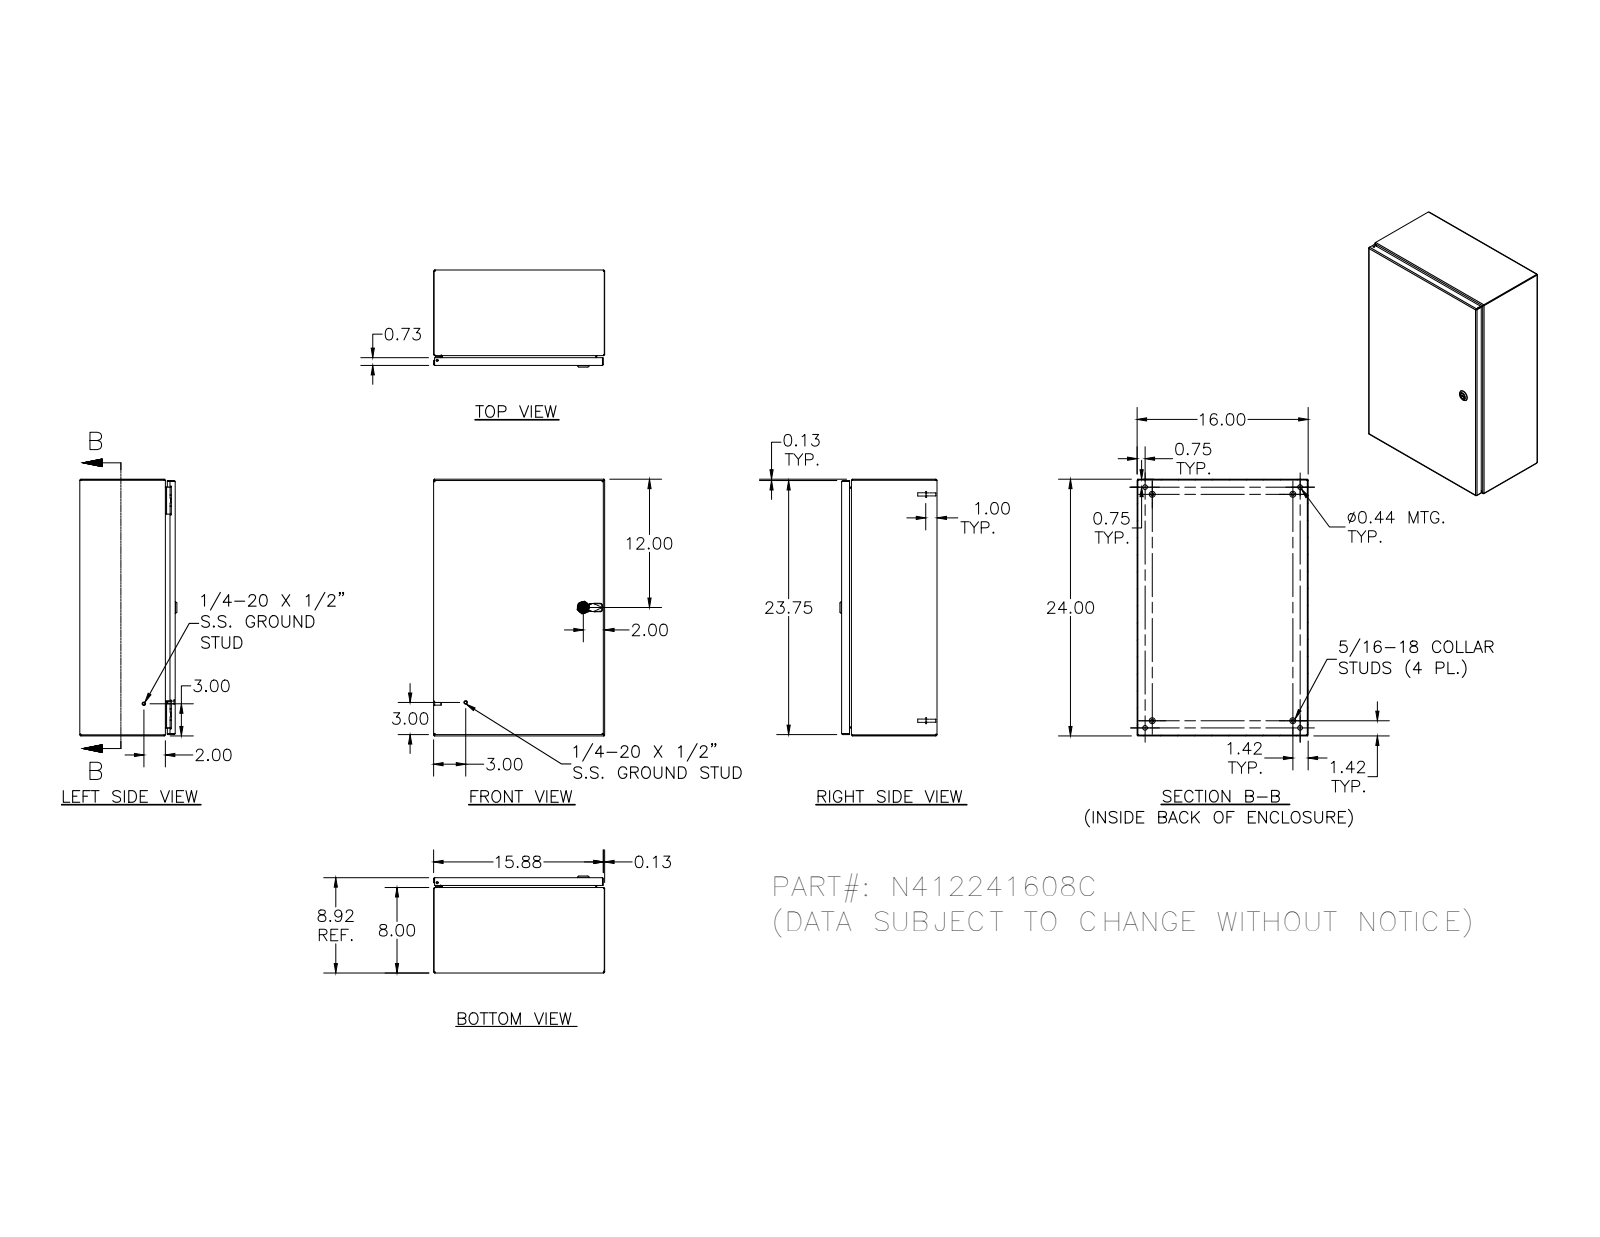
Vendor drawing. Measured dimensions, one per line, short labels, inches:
name: N412241608C
written by: SolidWorks 2018 (AUTOMOTIVE_DESIGN)
unit: in
bodies: 33 solids, 1449 faces (530 planar, 547 cylindrical, 372 other)
size: 24 × 16 × 9.075
volume: 116.2 in³; area: 3 160 in²
holes: 5× ⌀0.188, 4× ⌀0.093, 4× ⌀0.152, 4× ⌀0.167, 4× ⌀0.172, 4× ⌀0.437, 2× ⌀0.156, 1× ⌀0.187, 1× ⌀0.197, 1× ⌀0.315, 1× ⌀0.394, 1× ⌀0.402
bosses: 10× ⌀0.25, 4× ⌀0.563, 4× ⌀0.36, 4× ⌀0.32, 4× ⌀0.3, 4× ⌀0.256, 4× ⌀0.164, 4× ⌀0.131
rounds: 30× R0.012, 30× R0.031, 26× R0.05, 20× R0.105, 18× R0.016, 16× R0.125, 13× R0.02, 8× R0.032
face distances: 0.074, 8.843, 8.769, 8.917, 0.074, 15.926, 16, 15.852, 15.926, 23.926
hole spacings: 20, 0.66, 0.656, 1.307, 1.965, 0.5, 0.984, 1.311
